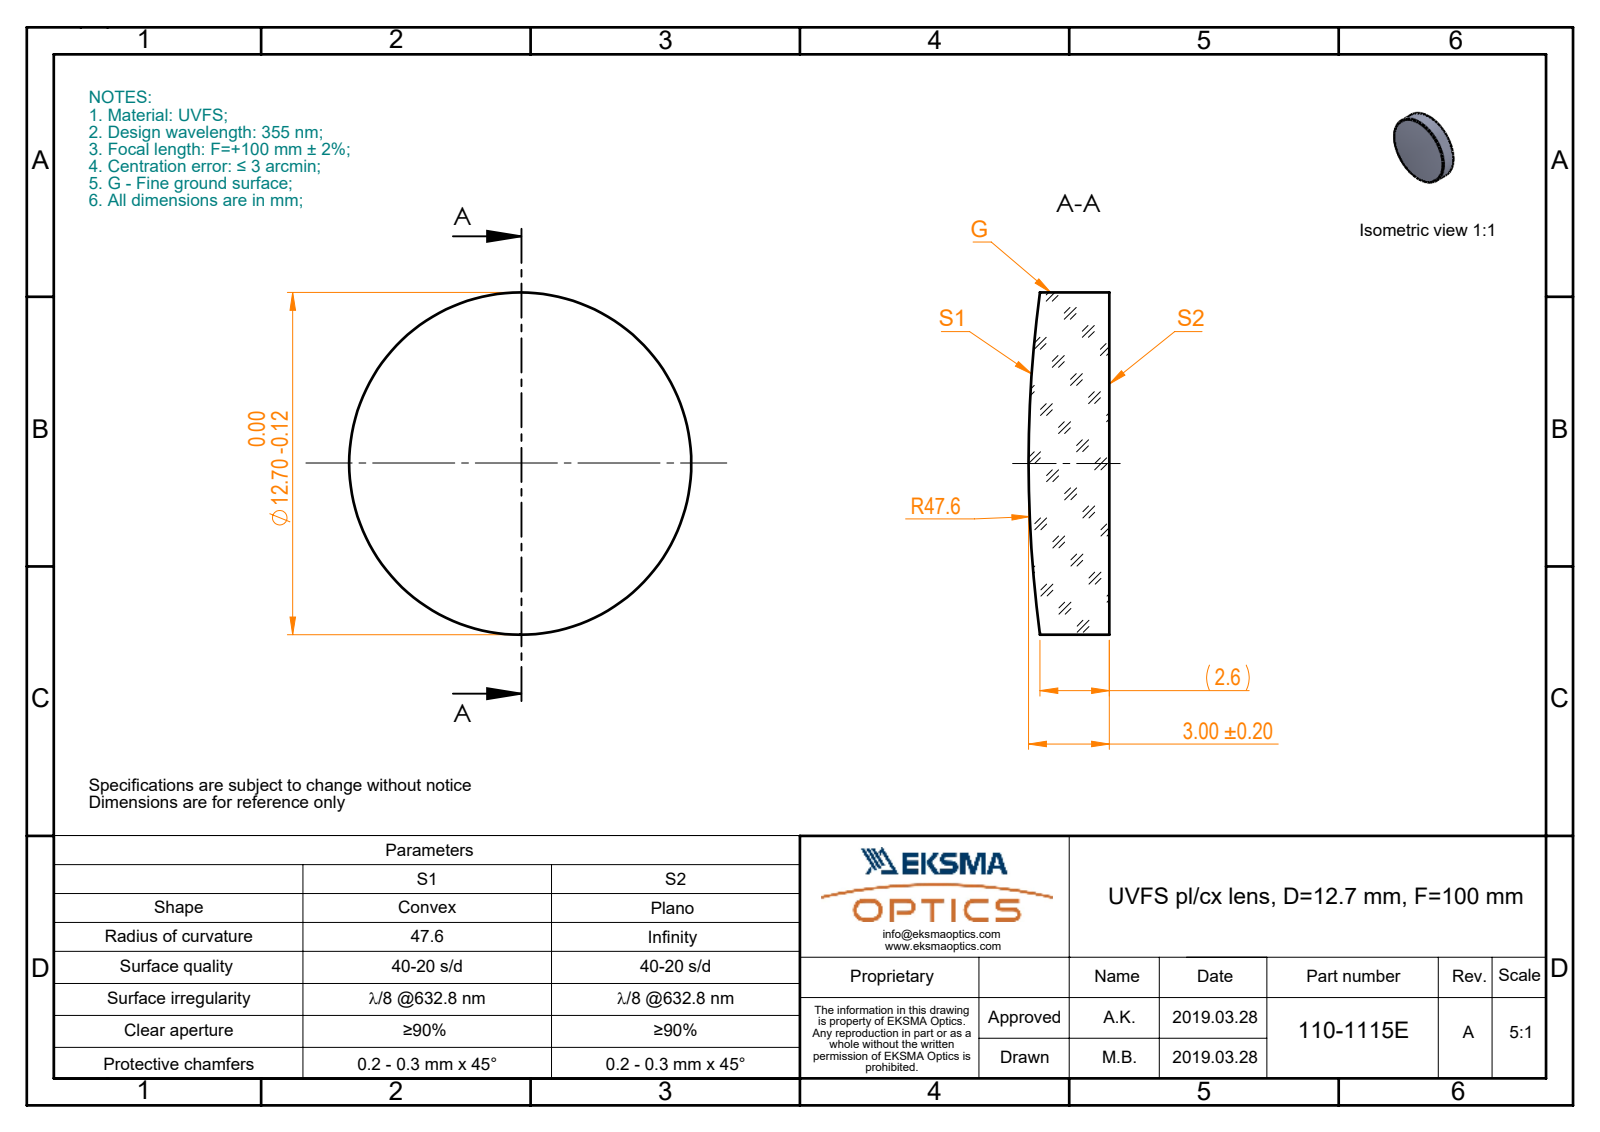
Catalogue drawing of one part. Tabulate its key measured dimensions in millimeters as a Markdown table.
| quantity | value |
| --- | --- |
| part name | 110-1115E UVFS pl-cx 12.7 F100 |
| STEP written by | SolidWorks 2017 (CONFIG_CONTROL_DESIGN) |
| units | millimeters |
| bodies | 1 solid, 5 faces (1 planar, 2 cylindrical, 2 other) |
| overall size | 12.7 × 12.7 × 3 |
| volume | 353 mm³ |
| surface area | 357 mm² |
| round bosses / shafts (diameter × count) | 12.7 × 1 |
